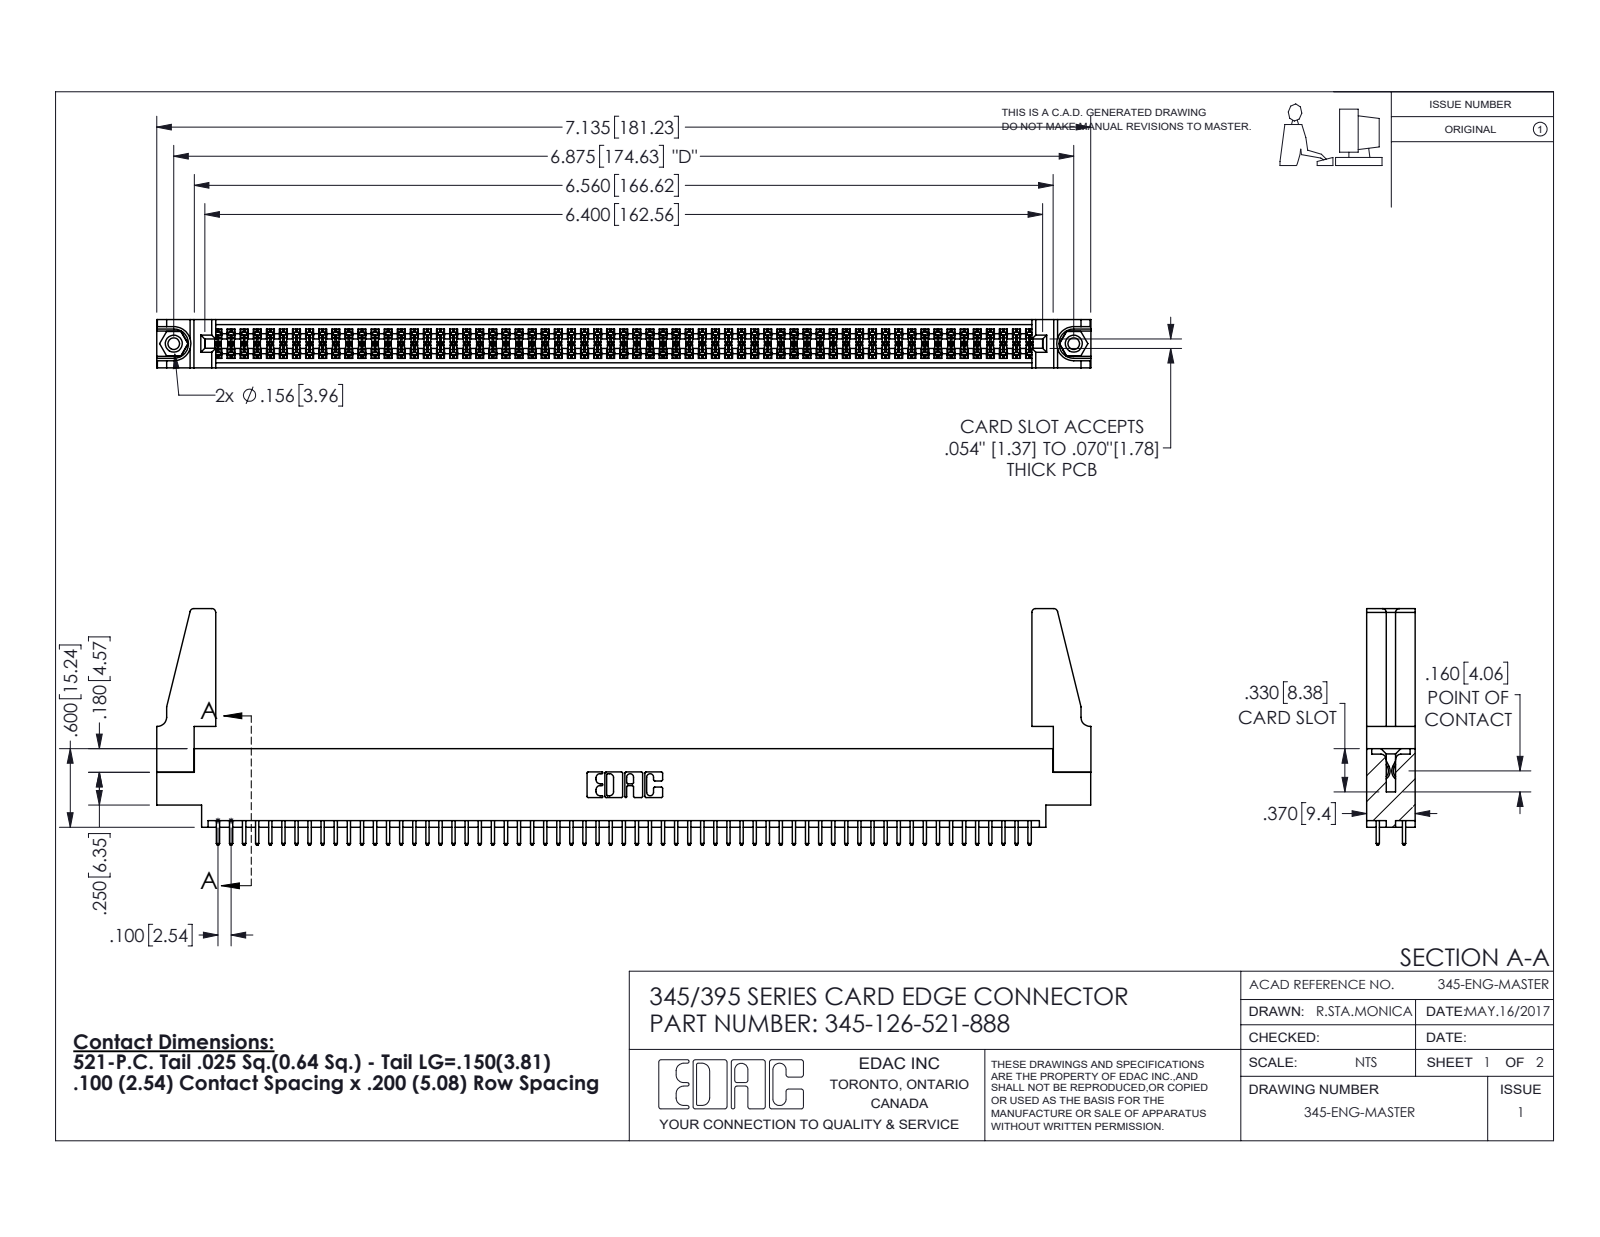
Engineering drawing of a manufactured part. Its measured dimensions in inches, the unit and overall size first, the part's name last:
Units: inches
Overall size (bounding box): 7.136 × 1.807 × 0.37
Round holes (diameter × count): ⌀0.089 ×2, ⌀0.125 ×2, ⌀0.156 ×2, ⌀0.064 ×1
Round bosses / shafts (diameter × count): ⌀0.155 ×2
Partial cylindrical surfaces — rounded edges, fillets, slot ends (radius × count): R0.006 ×189, R0.01 ×126, R0.01 ×22, R0.03 ×8, R0.007 ×6, R0.031 ×6, R0.026 ×3, R0.014 ×2
Main face-to-face distances: 0.072, 0.298, 0.37, 0.2, 0.098, 0.272, 0.025, 0.225, 0.175, 0.149
Hole centre spacings: 0.27, 6.639, 6.875
Volume: 1.275 in³ · Surface area: 45.58 in²
Bodies: 131 solids, 6554 faces (4314 planar, 2224 cylindrical, 16 other)
Part name (STEP PRODUCT): 345-292-001_345-293-121; 345 Part_0.170 Offset - 0.156 Dia-TH; 345-126-521-888; 345-250-001_345-250-001-102 (+1 more)
STEP written by: SolidWorks 2016 (CONFIG_CONTROL_DESIGN)
